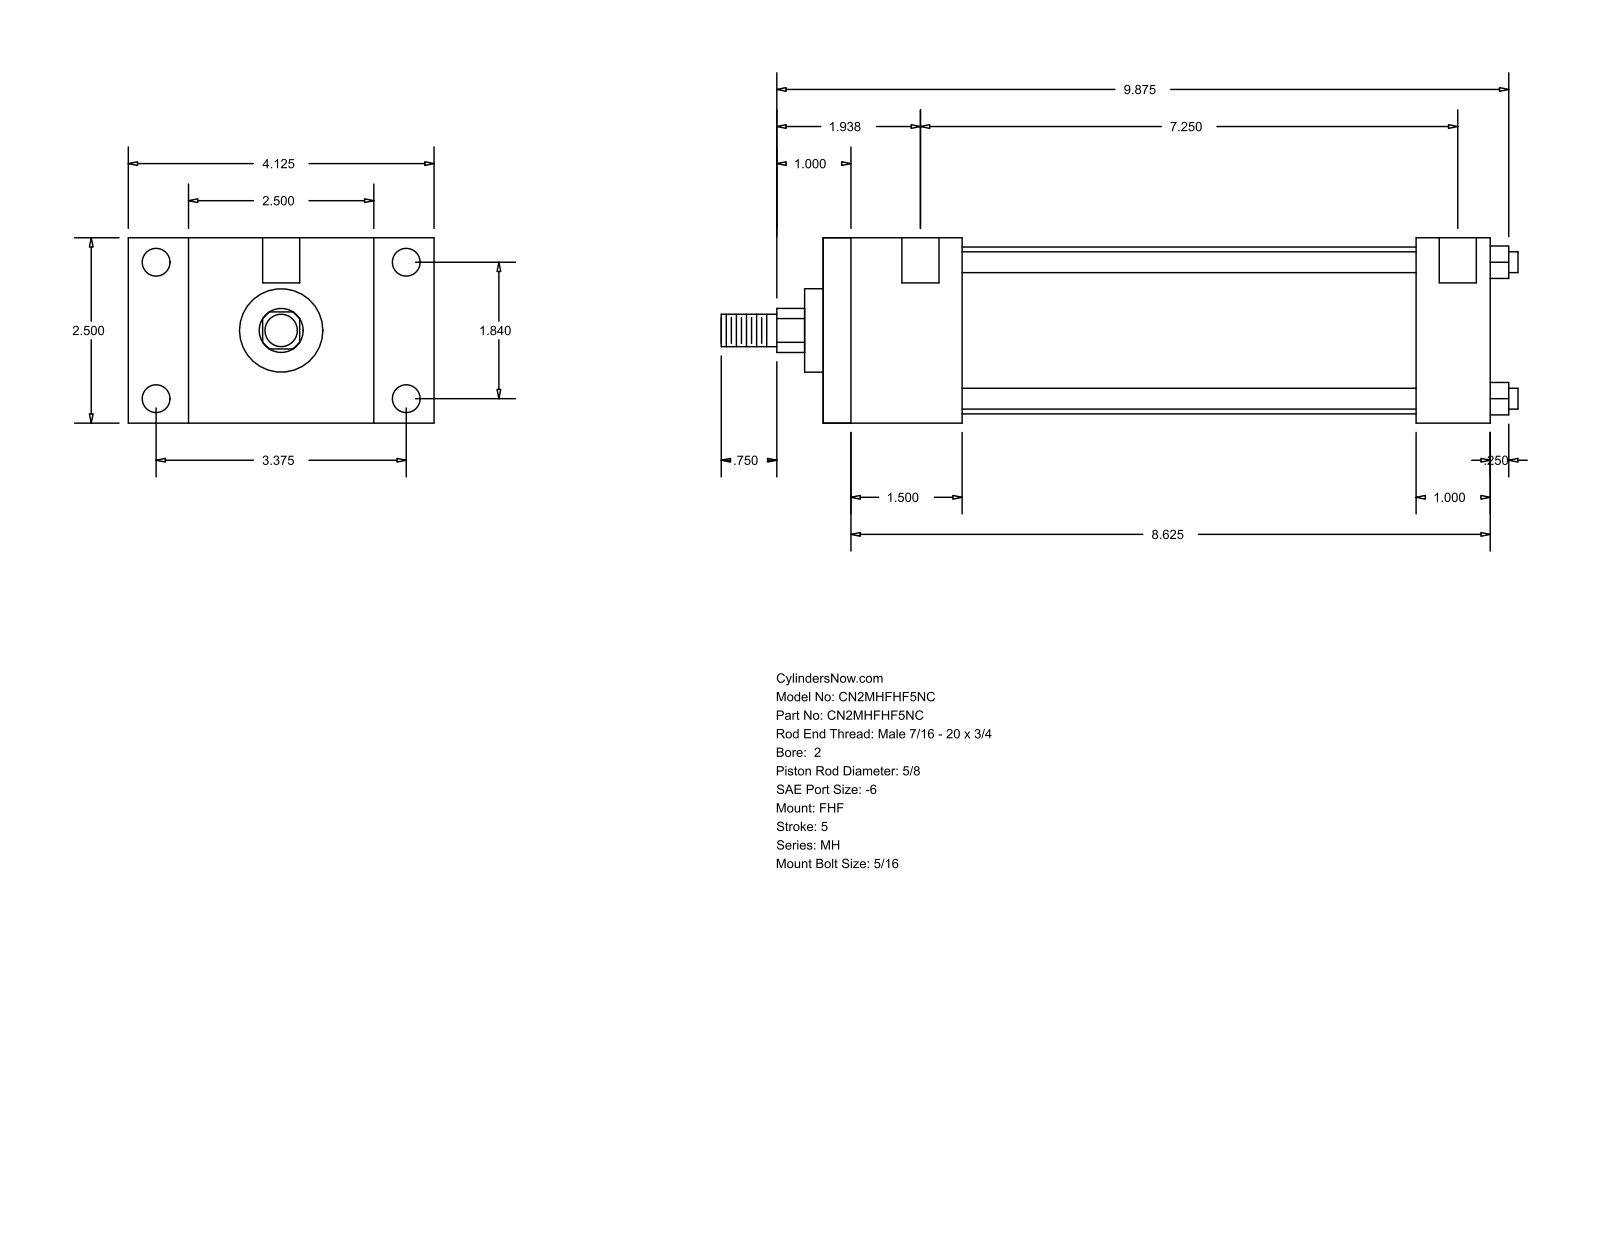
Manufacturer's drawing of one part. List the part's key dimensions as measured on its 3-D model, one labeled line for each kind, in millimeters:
Part name (STEP PRODUCT): MH_FHF__0200_0.625
STEP written by: GSSL Pune (CONFIG_CONTROL_DESIGN)
Units: millimetres
Bodies: 0 solids, 88 faces (60 planar, 28 cylindrical, 0 other)
Overall size (bounding box): 273.05 × 104.78 × 63.5
Round holes (diameter × count): ⌀5.56 ×4, ⌀9.53 ×4, ⌀12.7 ×2
Round bosses / shafts (diameter × count): ⌀7.14 ×4, ⌀57.15 ×1, ⌀28.57 ×1, ⌀15.88 ×1, ⌀11.11 ×1
Partial cylindrical surfaces — rounded edges, fillets, slot ends (radius × count): R7.54 ×1
Main face-to-face distances: 63.5, 47.62, 228.59, 180.97, 20.64, 84.14, 104.78, 25.4, 203.19, 155.57
Hole centre spacings: 46.74, 85.72, 97.63, 192.09, 3.18, 4.76, 184.15, 187.33
